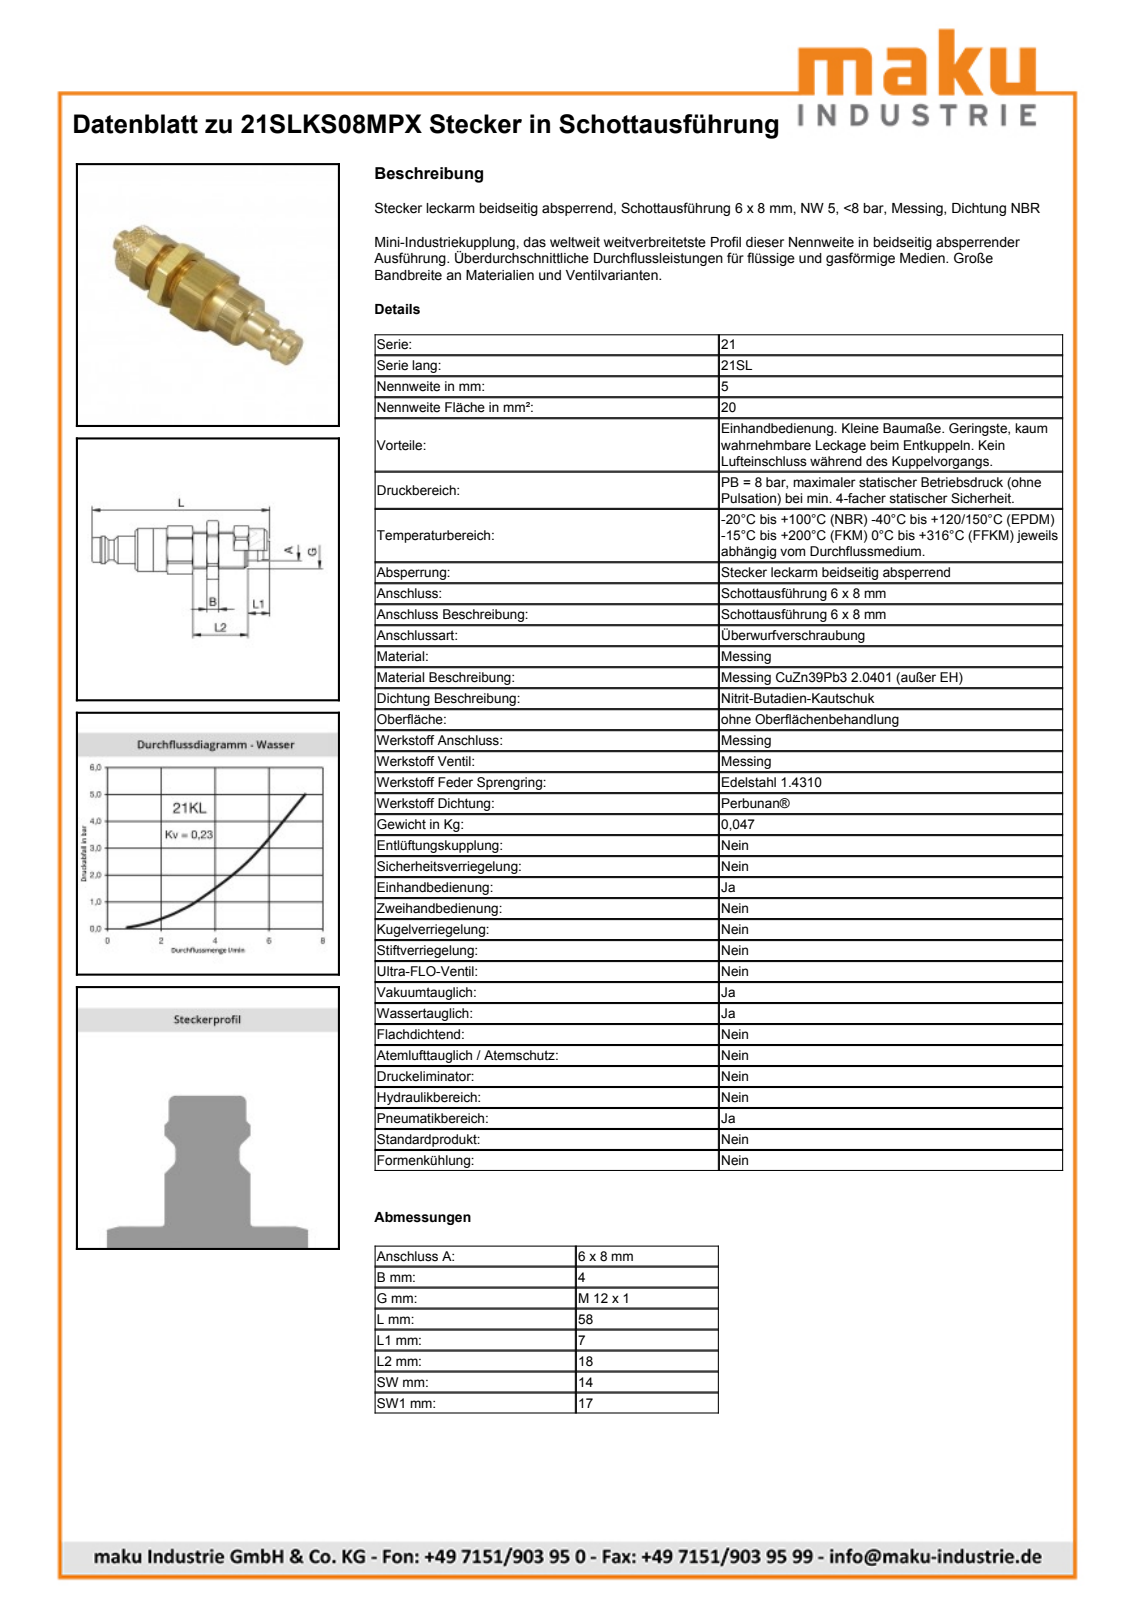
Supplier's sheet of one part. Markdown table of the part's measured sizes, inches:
| quantity | value |
| --- | --- |
| part name | D113606 |
| STEP written by | Autodesk Inventor 2013 (AUTOMOTIVE_DESIGN) |
| units | inches |
| bodies | 1 solid, 125 faces (32 planar, 34 cylindrical, 59 other) |
| overall size | 2.283 × 0.754 × 0.746 |
| volume | 0.482 in³ |
| surface area | 6.346 in² |
| round holes (diameter × count) | 0.325 × 1, 0.439 × 1 |
| round bosses / shafts (diameter × count) | 0.551 × 1, 0.472 × 1, 0.472 × 1, 0.44 × 1, 0.354 × 1, 0.319 × 1, 0.264 × 1, 0.262 × 1 |
| partial cylindrical surfaces (radius × count) | 0.305 × 1, 0.377 × 1 |
| main face-to-face distances | 0.669, 0.157, 0.551, 0.401, 0.244, 0.337, 0.58, 0.738, 1.041, 0.705 |
